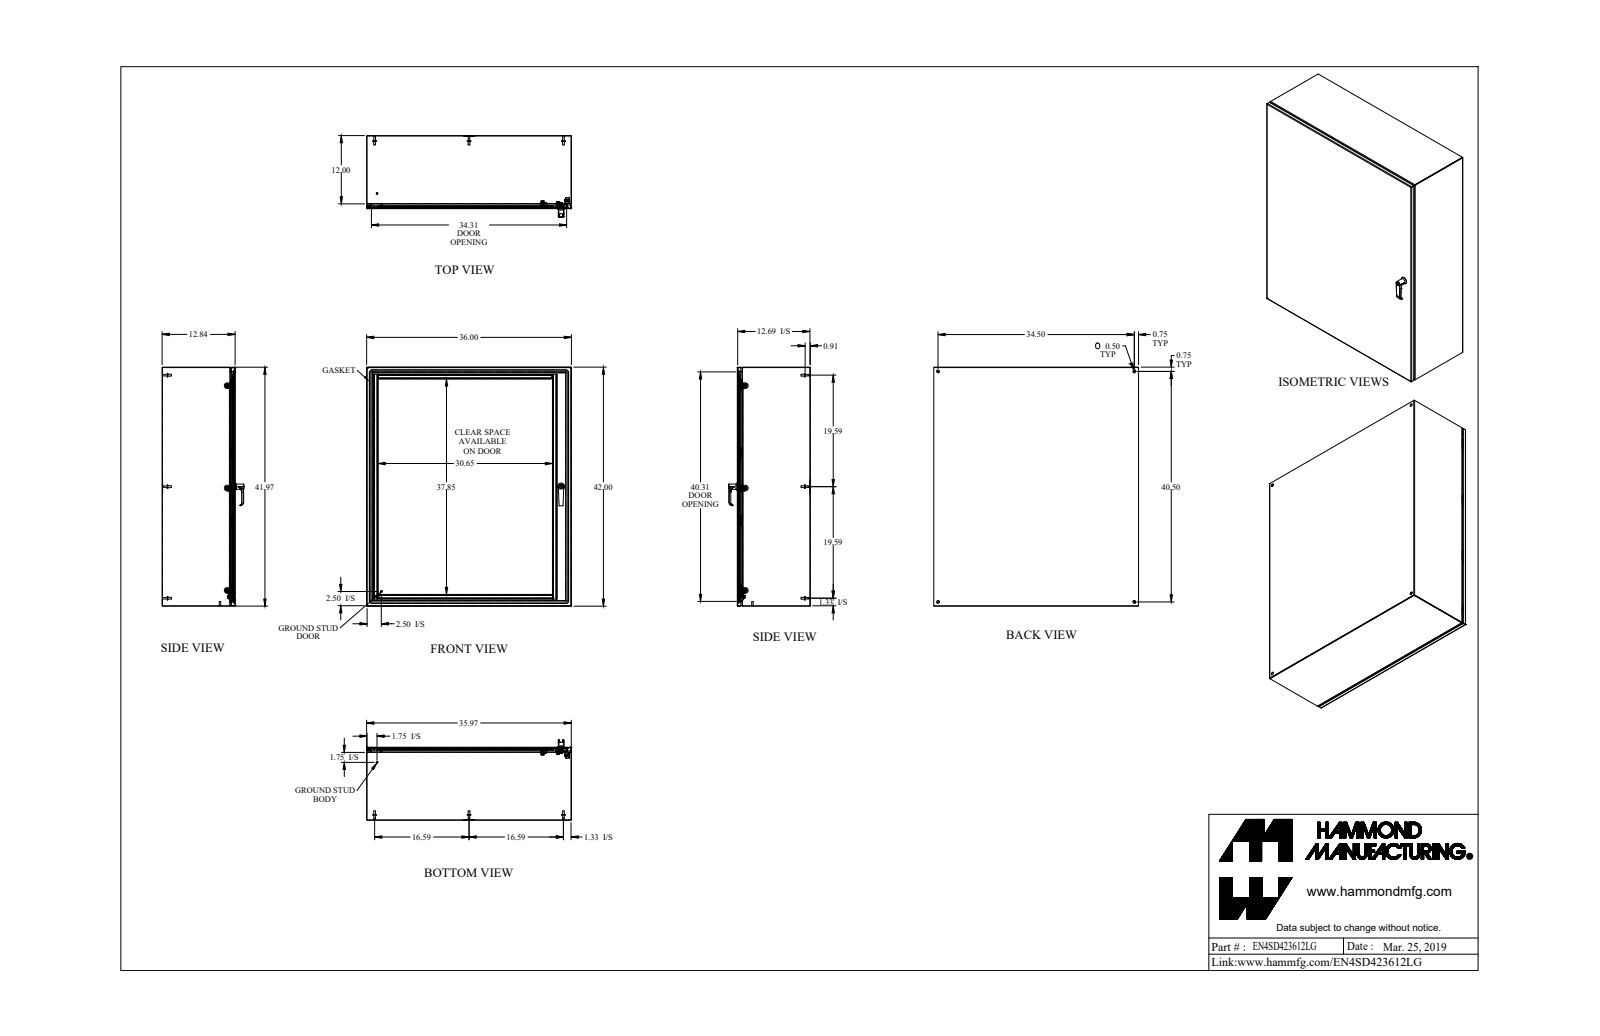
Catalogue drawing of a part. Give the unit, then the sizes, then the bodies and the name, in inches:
Units: inches
Overall size (bounding box): 42 × 36 × 14.367
Round holes (diameter × count): ⌀0.176 ×6, ⌀0.196 ×4, ⌀0.5 ×4, ⌀0.25 ×3, ⌀0.265 ×3, ⌀0.413 ×3, ⌀0.256 ×2, ⌀0.313 ×2, ⌀0.394 ×2, ⌀0.172 ×1, ⌀0.24 ×1, ⌀0.242 ×1
Round bosses / shafts (diameter × count): ⌀0.313 ×8, ⌀0.27 ×8, ⌀0.625 ×7, ⌀0.25 ×7, ⌀0.375 ×6, ⌀0.156 ×6, ⌀1 ×3, ⌀0.63 ×2
Partial cylindrical surfaces — rounded edges, fillets, slot ends (radius × count): R0.043 ×24, R0.081 ×24, R0.036 ×18, R0.108 ×18, R0.03 ×15, R0.062 ×13, R0.094 ×10, R0.016 ×9
Main face-to-face distances: 0.072, 12.765, 12.693, 12.837, 35.928, 41.928, 35.856, 36, 41.856, 42
Hole centre spacings: 0.787, 35.969, 17.981, 17.988, 18, 33.504, 34.5, 40.5
Volume: 408.9 in³ · Surface area: 11 443 in²
Bodies: 63 solids, 1719 faces (757 planar, 632 cylindrical, 330 other)
Part name (STEP PRODUCT): EN4SD423612LG
STEP written by: SolidWorks 2018 (AUTOMOTIVE_DESIGN)
